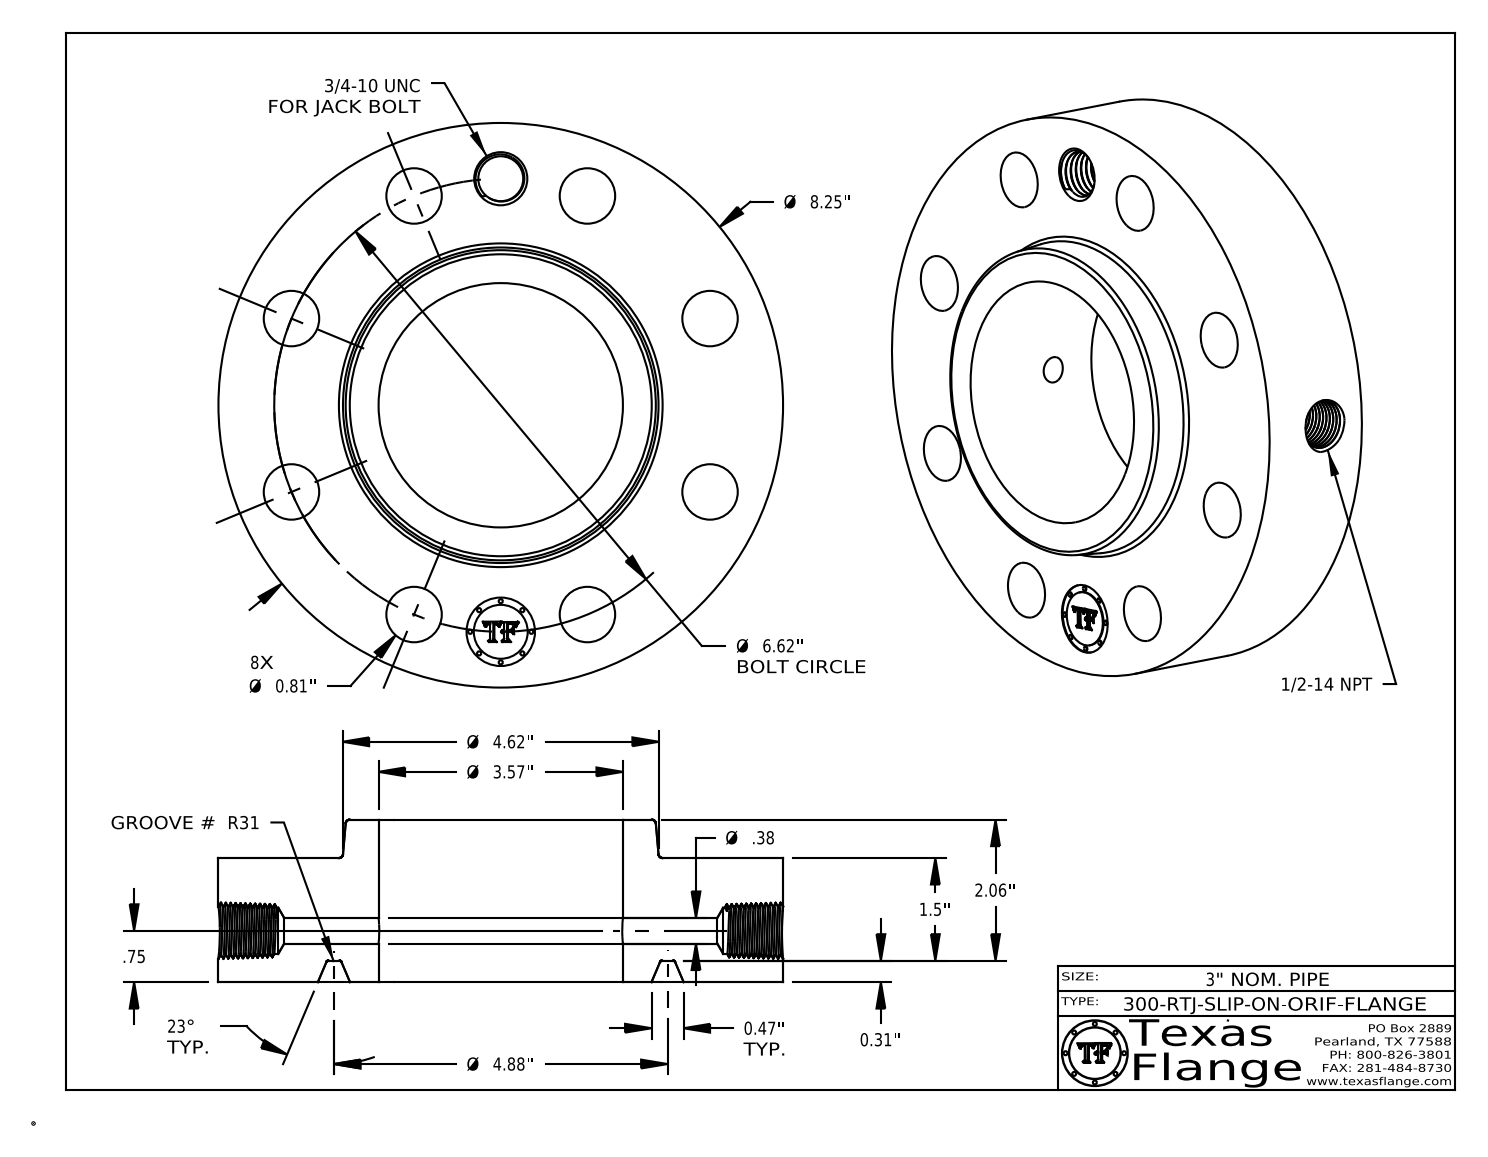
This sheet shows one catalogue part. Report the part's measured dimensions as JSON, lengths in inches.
{"part_name": "300-RTJ-SLIP-ON", "step_written_by": "CATIA V5 STEP AP214 (AUTOMOTIVE_DESIGN)", "units": "inches", "bodies": {"solids": 1, "faces": 793, "planar": 370, "cylindrical": 94, "other": 329}, "overall_size": [8.25, 8.25, 2.373], "volume_in3": 71.48, "surface_area_in2": 216.8, "round_holes": [[0.81, 8], [0.375, 1], [0.656, 1], [0.672, 1], [1, 1], [3.57, 1]], "round_bosses_or_shafts": [[0.061, 8], [8.25, 1], [0.788, 1]], "face_to_face_distances": [1.813, 2.373, 0.56, 0.313, 1.5, 2.06, 0.015, 1.798, 1.485, 0.575], "hole_center_spacings": [3.31, 4.681, 6.116, 6.62, 1.291, 2.533, 2.533, 3.678]}
